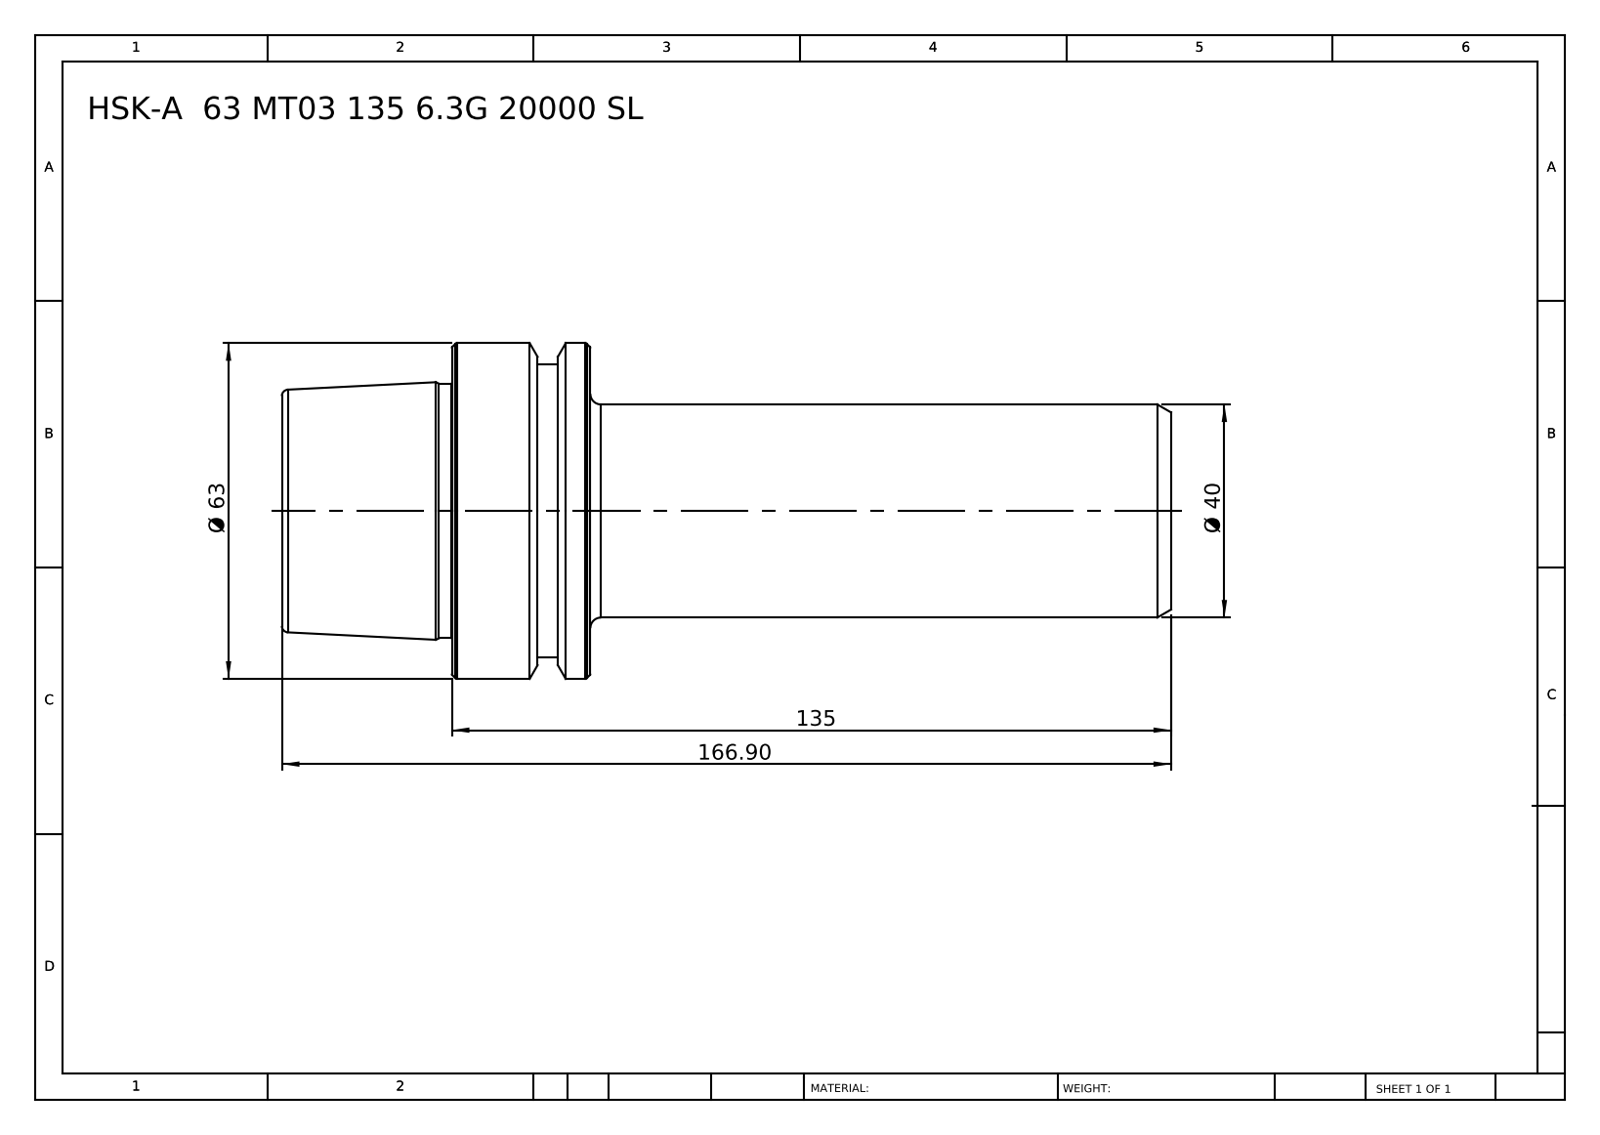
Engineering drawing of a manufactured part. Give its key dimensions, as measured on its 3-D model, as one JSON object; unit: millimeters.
{"part_name": "HSK-A 63 MT03 135 6.3G 20000 SL", "step_written_by": "SolidWorks 2014 (CONFIG_CONTROL_DESIGN)", "units": "millimeters", "bodies": {"solids": 1, "faces": 46, "planar": 6, "cylindrical": 10, "other": 30}, "overall_size": [166.9, 63, 63], "volume_mm3": 269417, "surface_area_mm2": 30093, "round_bosses_or_shafts": [[63, 1], [55, 1], [47.78, 1], [40, 1]], "face_to_face_distances": [57.9, 109, 166.9, 135, 26, 31.9, 115.1, 6.1, 19.9, 51.8]}
